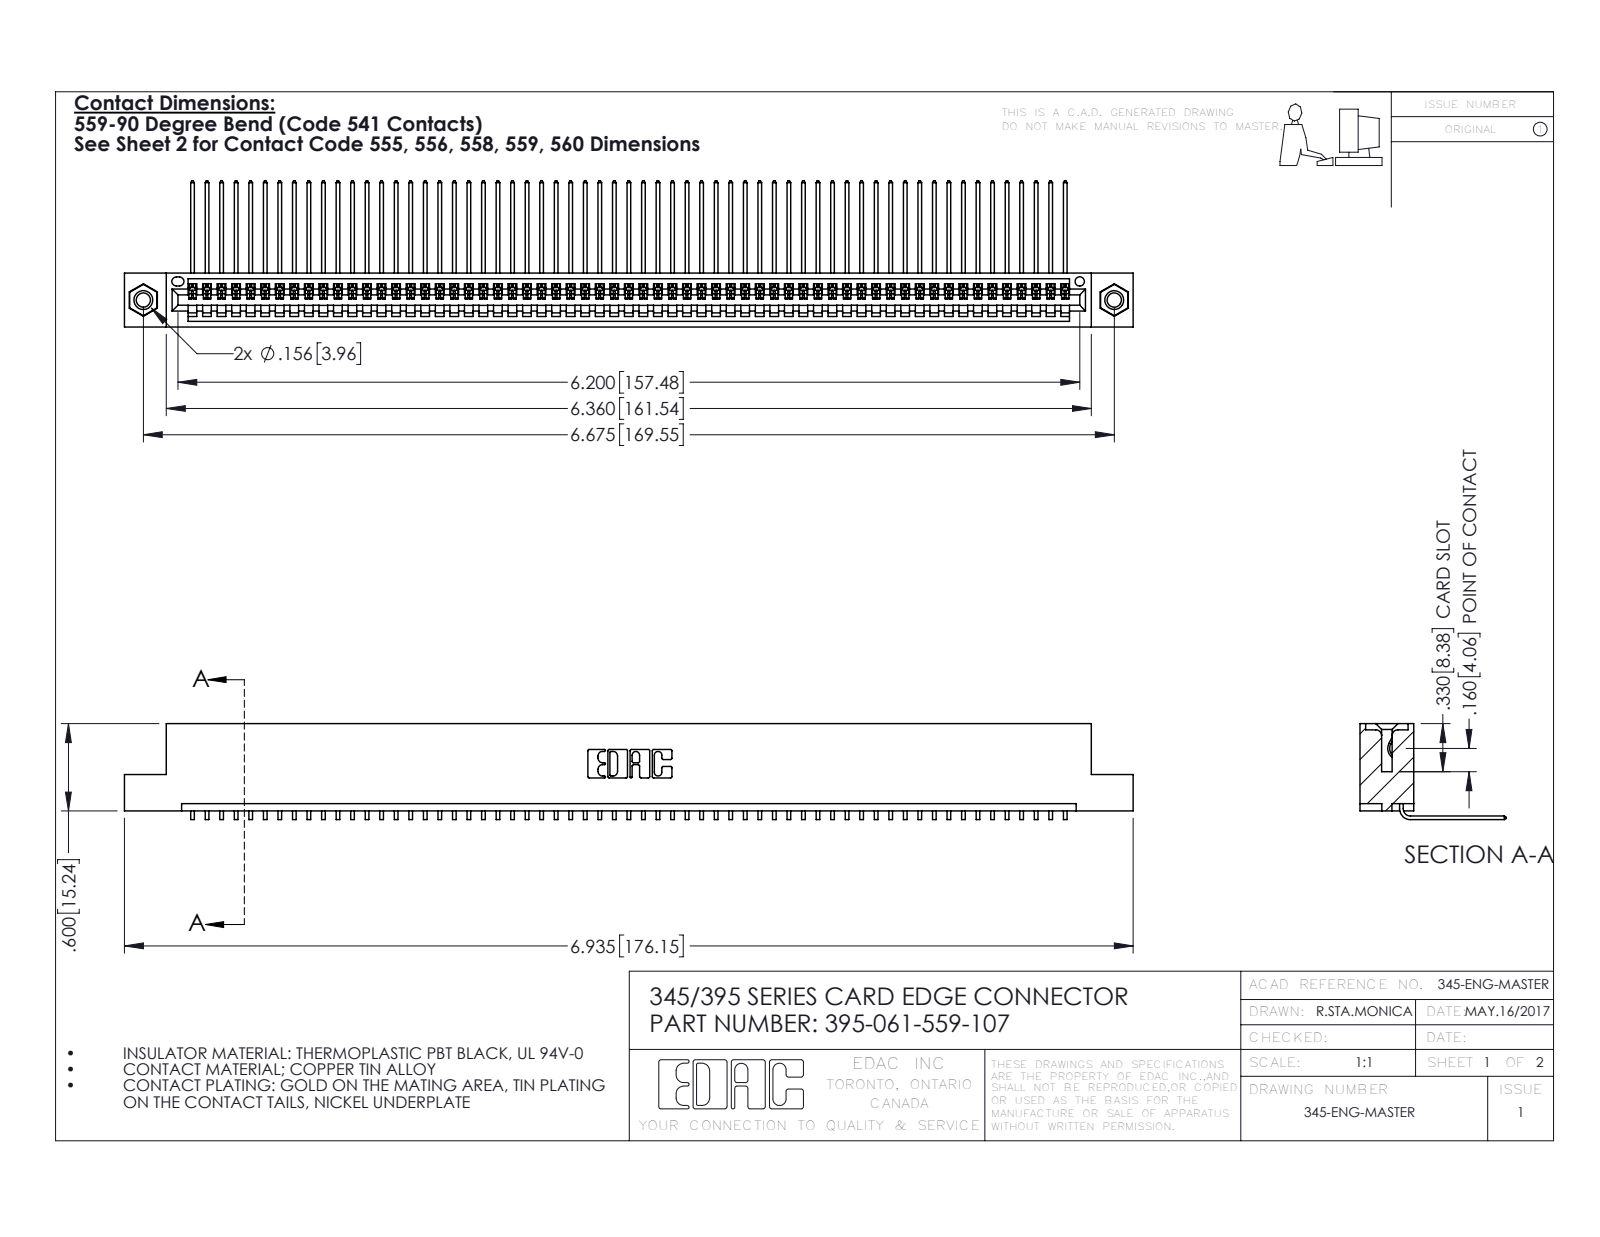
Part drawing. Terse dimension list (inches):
name: 395-061-559-107; 345 Part_Flush Mounting Lugs - 0.156 Dia-TI; 345-250-001_345-250-005-103; 345-292-001_558 559 Tail - 1
written by: SolidWorks 2016 (CONFIG_CONTROL_DESIGN)
unit: in
bodies: 64 solids, 3846 faces (2674 planar, 1156 cylindrical, 16 other)
size: 6.935 × 1.005 × 0.659
volume: 1.042 in³; area: 37.48 in²
holes: 2× ⌀0.098, 2× ⌀0.125, 2× ⌀0.156, 1× ⌀0.064
bosses: 2× ⌀0.155
rounds: 122× R0.006, 22× R0.01, 6× R0.007, 6× R0.031, 3× R0.026, 2× R0.031, 2× R0.04, 1× R0.014
face distances: 0.072, 0.298, 0.37, 0.2, 0.098, 0.272, 0.025, 0.225, 0.149, 0.072
hole spacings: 0.27, 6.439, 6.675
